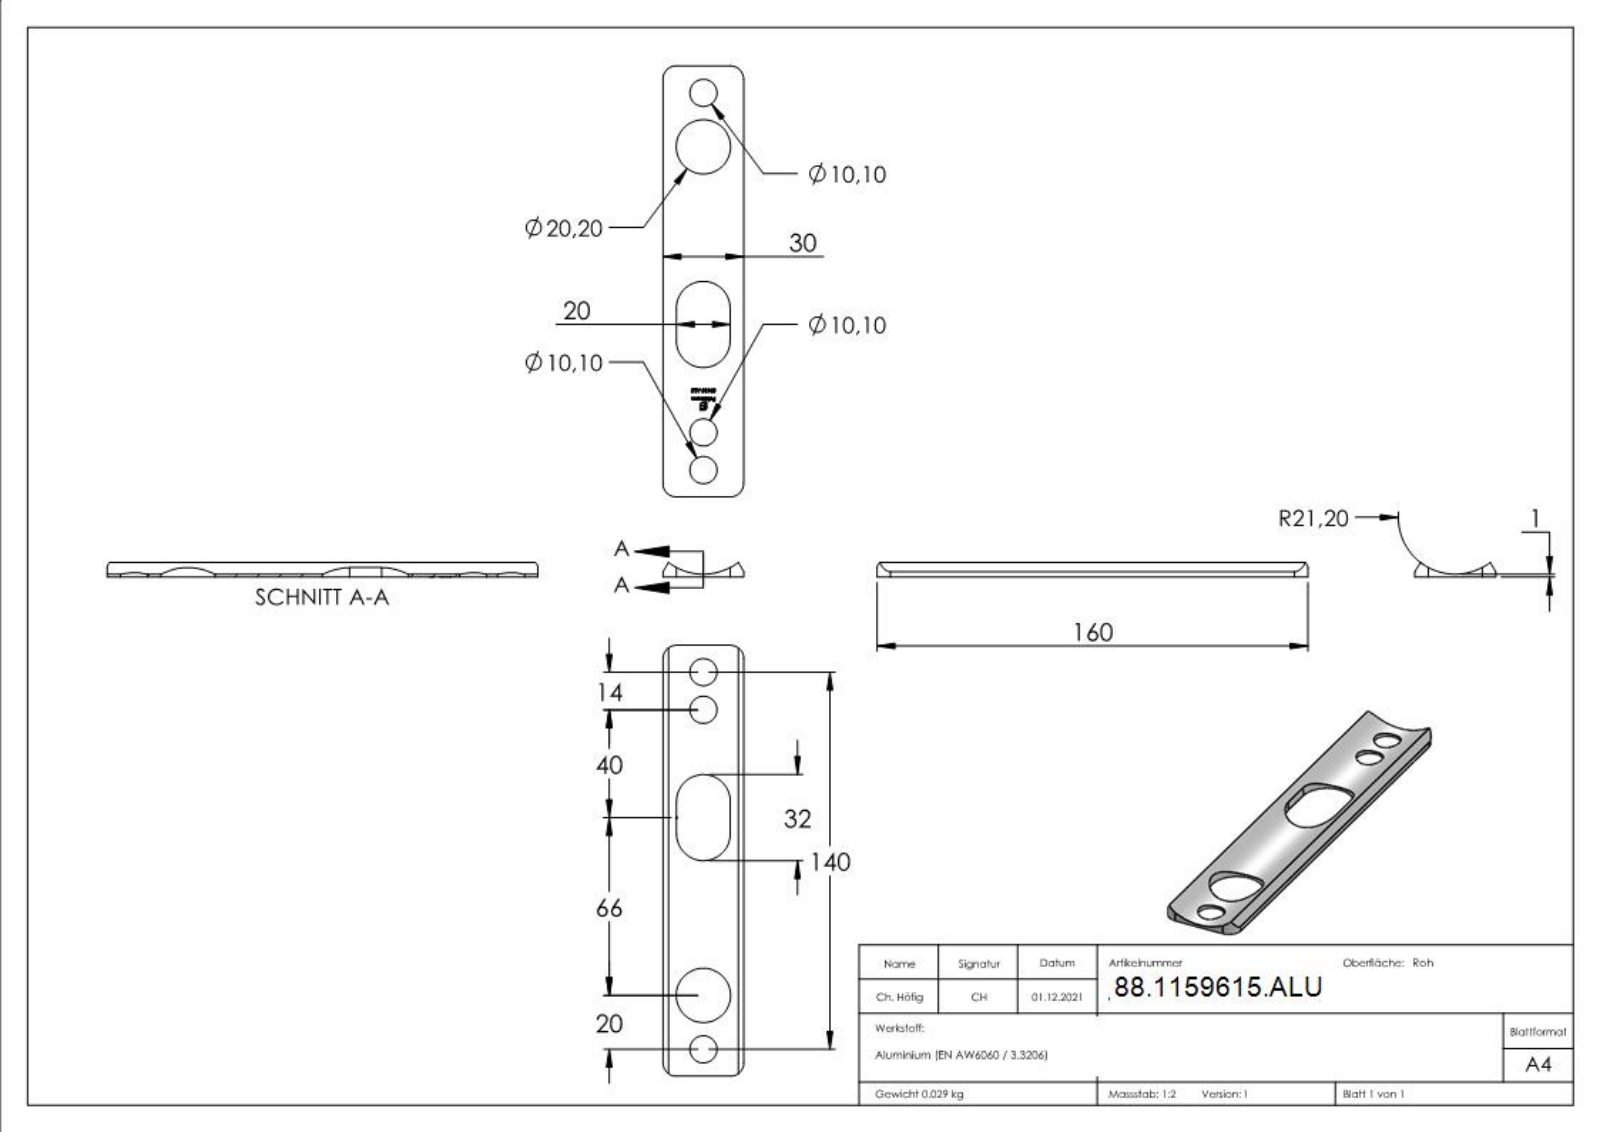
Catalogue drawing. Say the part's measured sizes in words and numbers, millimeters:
The part is named "59615-ALU". Its 3-D file was written by "SolidWorks 2018 (CONFIG_CONTROL_DESIGN)". It is 1 solid with 280 faces: 160 planar, 11 cylindrical and 109 other. Overall it measures 160 by 30 by 5.45 millimeters. Its volume is 10 621 cubic millimeters and its surface area 9 526 square millimeters. Round holes: 3 of diameter 10.1, 1 of diameter 20.2. Partial cylindrical surfaces (rounded edges, fillets, slot ends): 4 of radius 5, 2 of radius 10, 1 of radius 21.2. The main face-to-face distances are 30, 5, 25, 20, 160, 3.15, 3.71, 3.83, 0.32, 3.35. The hole center spacings are 14, 20, 106, 120, 126, 140.
